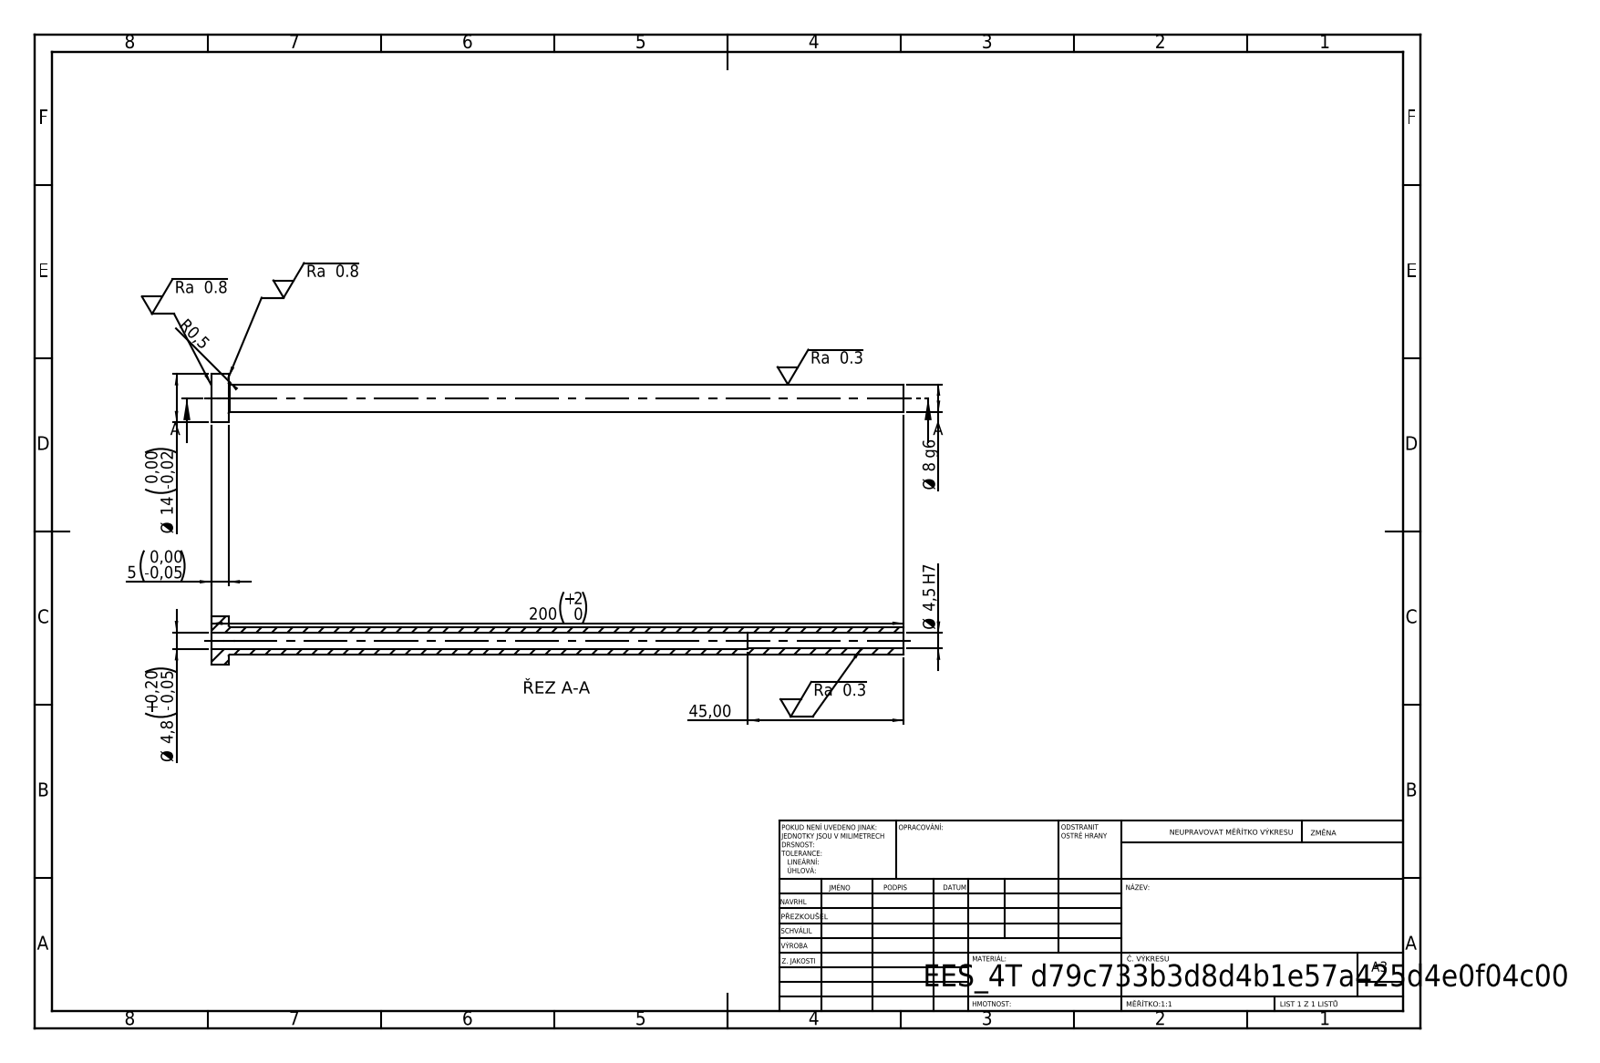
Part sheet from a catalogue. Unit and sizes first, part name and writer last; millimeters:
Units: millimetres
Overall size (bounding box): 200 × 14 × 14
Round holes (diameter × count): ⌀4.5 ×1, ⌀4.8 ×1
Round bosses / shafts (diameter × count): ⌀14 ×1, ⌀8 ×1
Main face-to-face distances: 5, 200, 195, 155, 150, 45
Volume: 7 052 mm³ · Surface area: 8 365 mm²
Bodies: 1 solid, 14 faces (4 planar, 8 cylindrical, 2 other)
STEP written by: SolidWorks 2019 (CONFIG_CONTROL_DESIGN)
